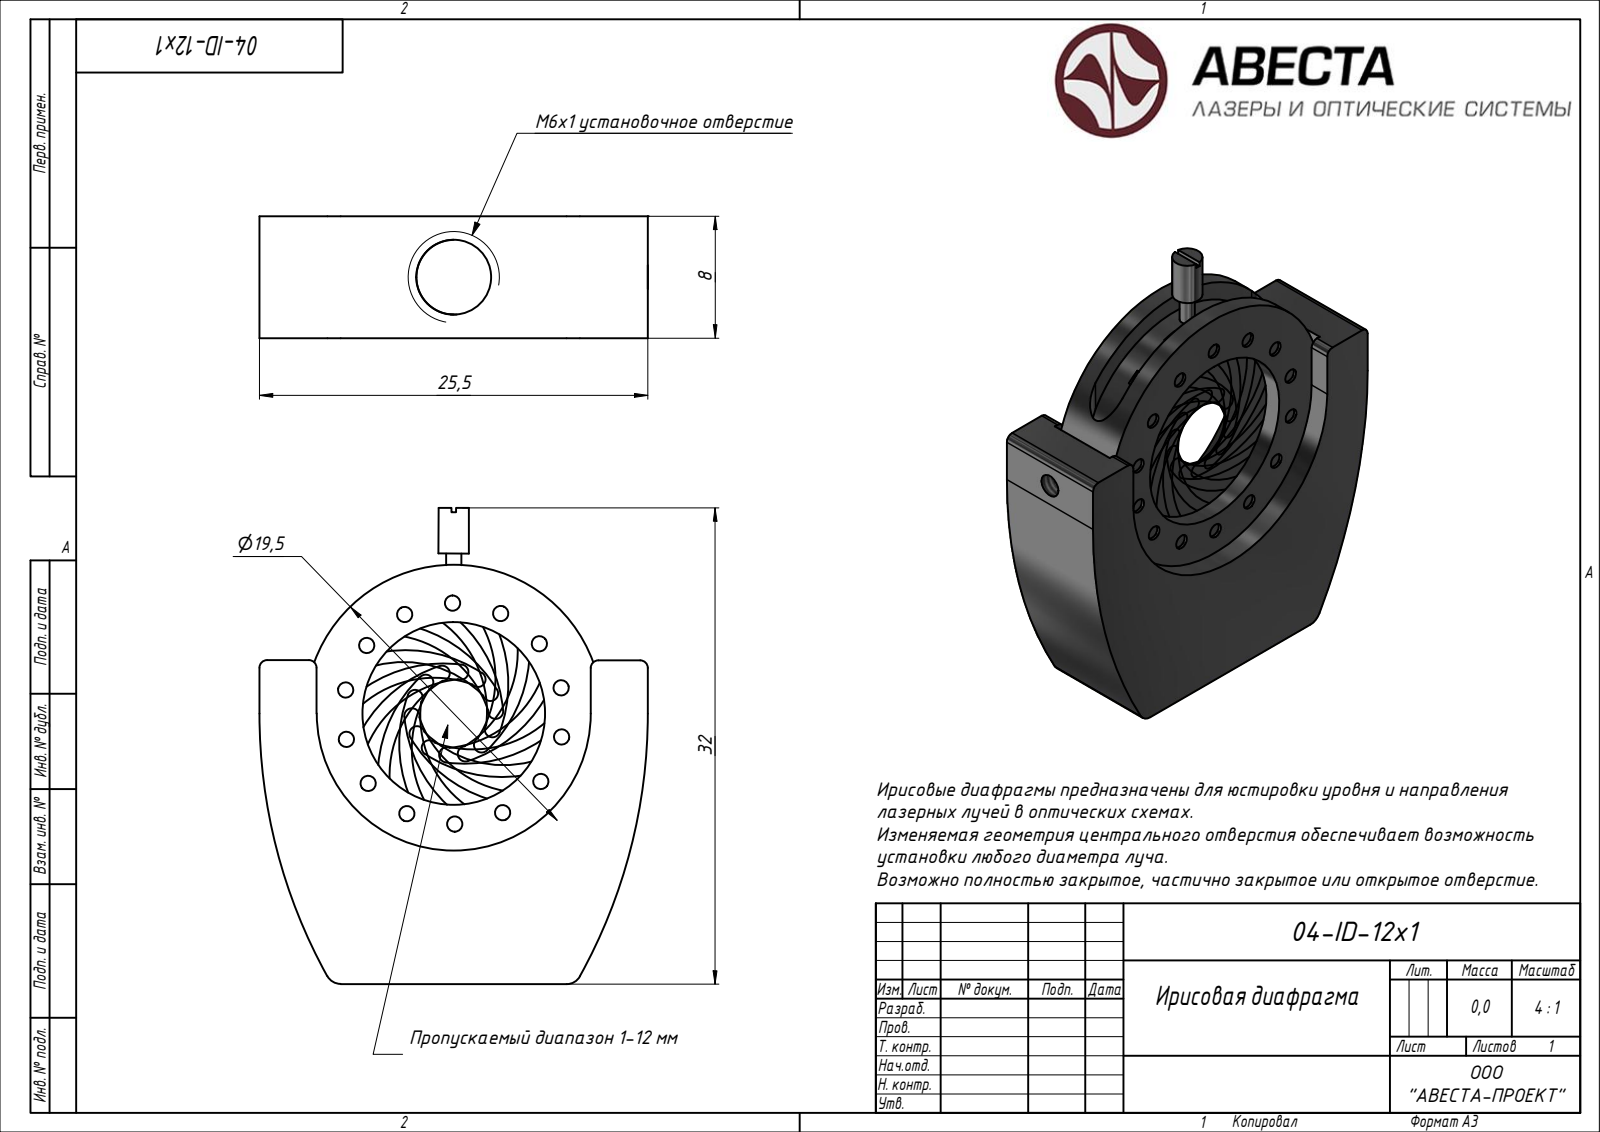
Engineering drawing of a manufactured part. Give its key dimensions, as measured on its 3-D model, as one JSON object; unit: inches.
{"step_written_by": "ST-DEVELOPER v15 (AUTOMOTIVE_DESIGN)", "units": "inches", "bodies": {"solids": 0, "faces": 347, "planar": 185, "cylindrical": 0, "other": 162}, "overall_size": [1.23, 1.004, 0.315], "face_to_face_distances": [0.315, 0.108, 0.207, 0.15, 0.057, 0.047, 0.258, 0.051, 0.098, 0.104]}
